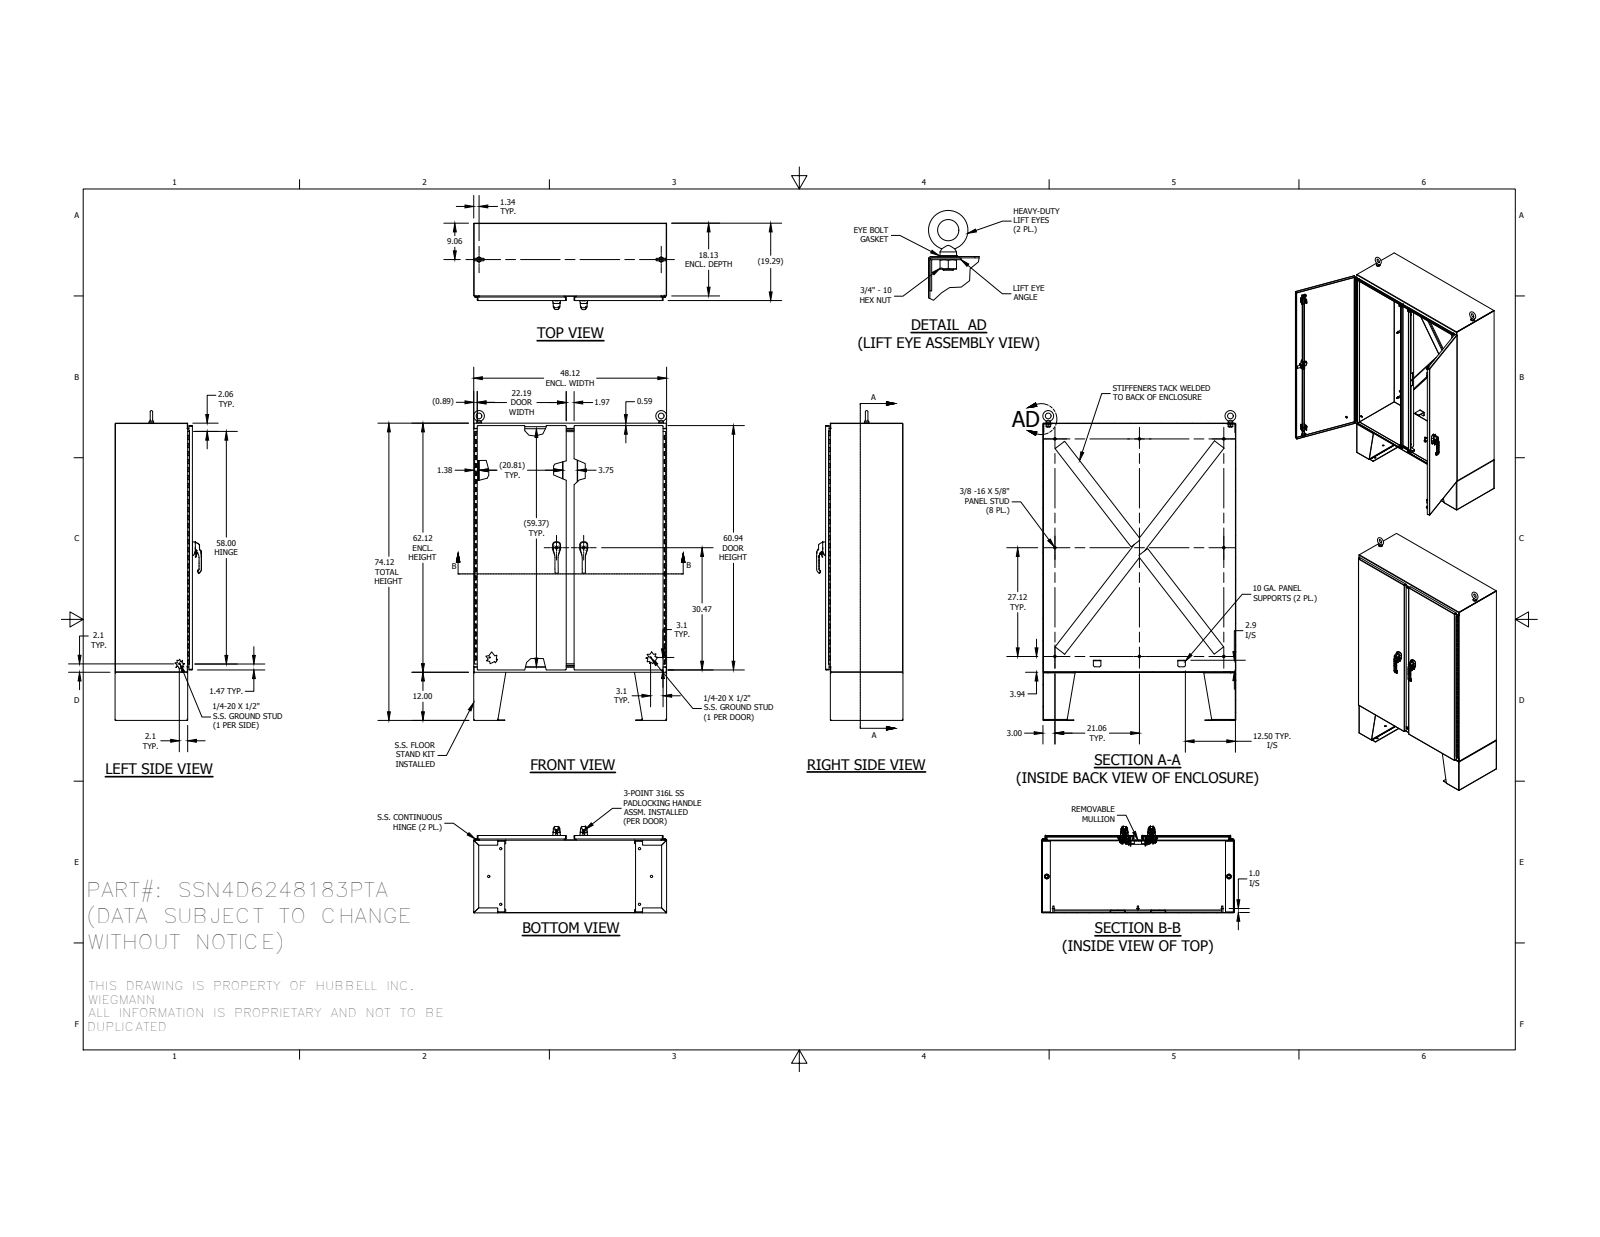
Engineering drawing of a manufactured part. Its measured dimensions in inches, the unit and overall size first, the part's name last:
Units: inches
Overall size (bounding box): 77.248 × 48.125 × 21.538
Round holes (diameter × count): ⌀0.563 ×18, ⌀0.262 ×16, ⌀0.375 ×16, ⌀0.187 ×8, ⌀0.213 ×6, ⌀0.281 ×6, ⌀0.25 ×5, ⌀0.196 ×4, ⌀0.241 ×4, ⌀0.252 ×4, ⌀0.281 ×4, ⌀0.315 ×4
Round bosses / shafts (diameter × count): ⌀0.33 ×10, ⌀0.625 ×8, ⌀0.25 ×7, ⌀0.533 ×6, ⌀0.236 ×6, ⌀1 ×5, ⌀0.563 ×4, ⌀0.531 ×4
Partial cylindrical surfaces — rounded edges, fillets, slot ends (radius × count): R0.02 ×342, R0.012 ×213, R0.125 ×46, R0.019 ×42, R0.05 ×34, R0.031 ×32, R0.079 ×28, R0.025 ×24
Main face-to-face distances: 0.094, 19.196, 19.193, 48.031, 62.031, 19.102, 19.1, 19.29, 0.096, 19.287
Hole centre spacings: 6.444, 0.38, 0.38, 0.76, 12.889, 46.321, 52.052, 52.427
Volume: 1 323 in³ · Surface area: 27 427 in²
Bodies: 138 solids, 7184 faces (2696 planar, 2772 cylindrical, 1716 other)
Part name (STEP PRODUCT): SSN4D6248183PTA; D125B_10_5_1; 37026_1; 30254_1 (+8 more)
STEP written by: SolidWorks 2014 (AUTOMOTIVE_DESIGN)
